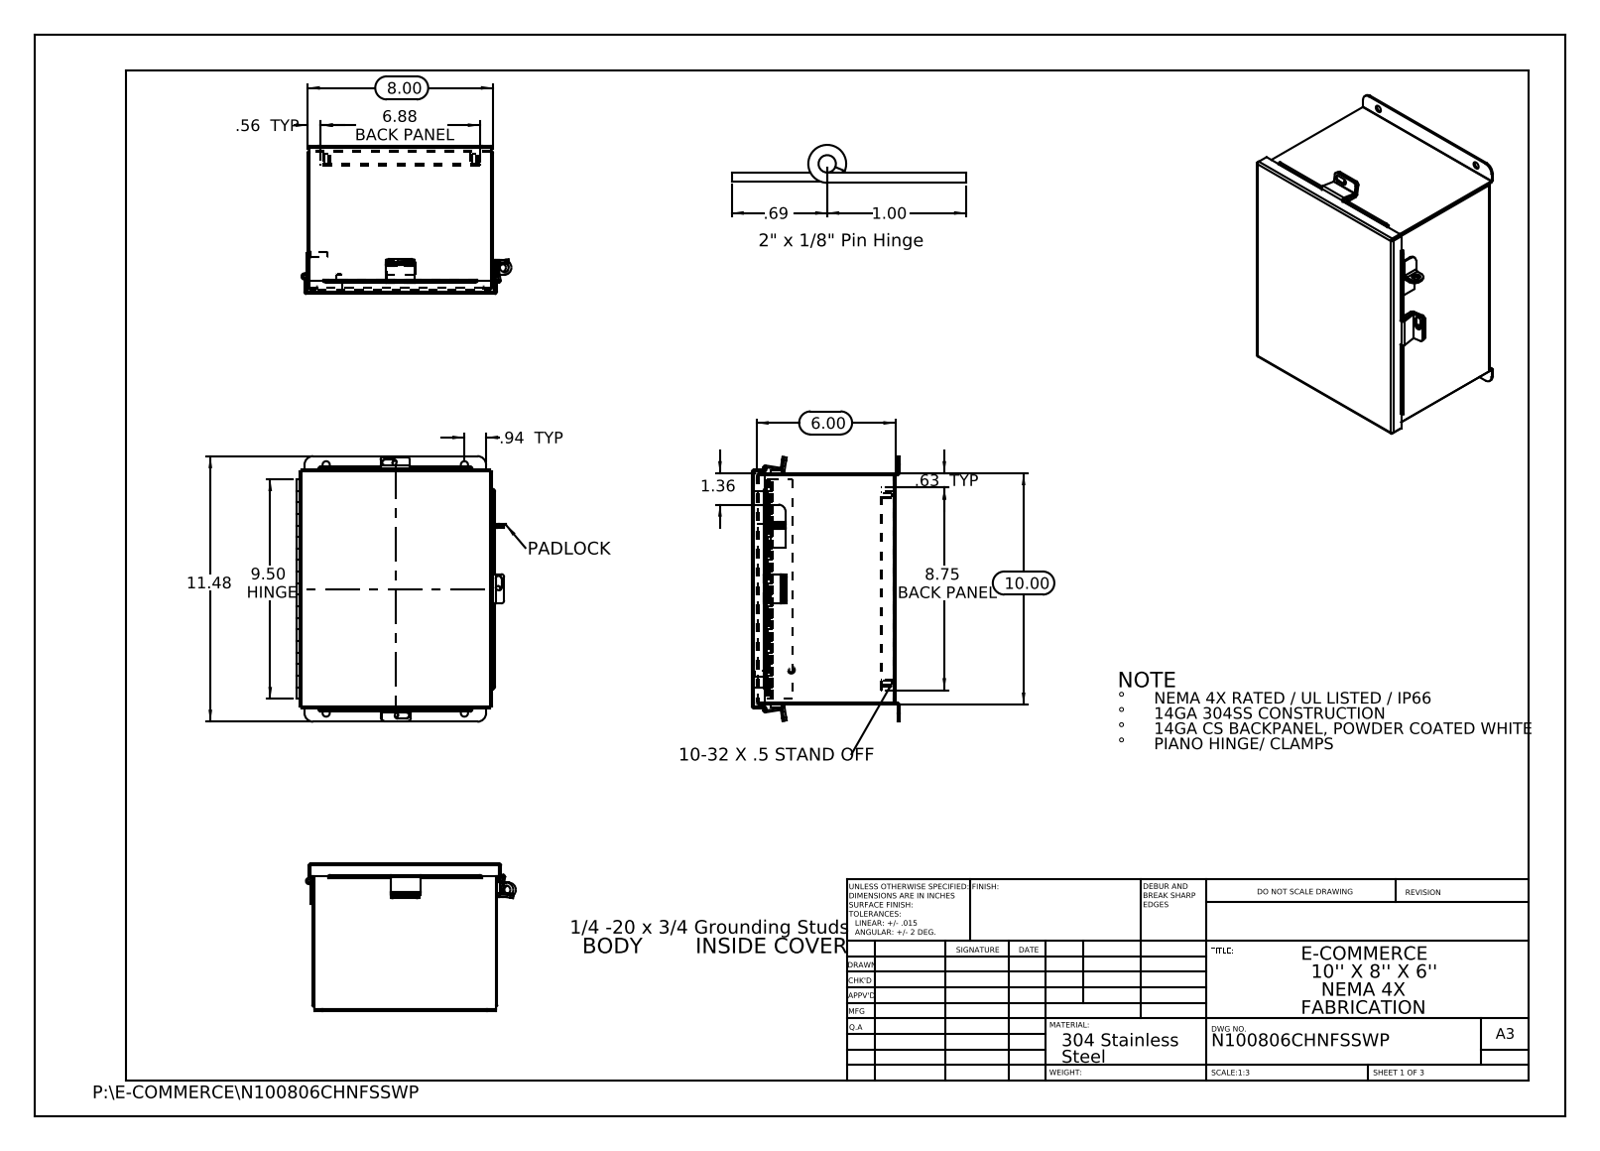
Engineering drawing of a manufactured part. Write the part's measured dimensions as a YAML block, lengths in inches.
part_name: "N100806CHNFSSWP Hinge Body Side; HW-CLH-JH-20104; N100806CHNFSSWP _JIC Hinge; N100806CHNFSSWP JIC Backpanel (+8 more)"
step_written_by: "SolidWorks 2013 (CONFIG_CONTROL_DESIGN)"
units: inches
bodies: {solids: 21, faces: 620, planar: 383, cylindrical: 217, other: 20}
overall_size: [11.476, 9.072, 6.39]
volume: 38.22
surface_area: 1047
round_holes:
  - {diameter: 0.25, count: 7}
  - {diameter: 0.187, count: 4}
  - {diameter: 0.312, count: 4}
  - {diameter: 0.125, count: 1}
  - {diameter: 0.373, count: 1}
  - {diameter: 0.375, count: 1}
round_bosses_or_shafts:
  - {diameter: 0.313, count: 4}
  - {diameter: 0.315, count: 2}
  - {diameter: 0.236, count: 2}
  - {diameter: 0.273, count: 1}
  - {diameter: 0.25, count: 1}
partial_cylinders:
  - {radius: 0.013, count: 13}
  - {radius: 0.009, count: 12}
  - {radius: 0.088, count: 12}
  - {radius: 0.125, count: 10}
  - {radius: 0.083, count: 6}
  - {radius: 0.1, count: 6}
  - {radius: 0.133, count: 6}
  - {radius: 0.375, count: 4}
face_to_face_distances: [0.075, 6.128, 7.925, 9.925, 6.053, 6.203, 0.074, 0.575, 0.5, 5.553]
hole_center_spacings: [1.315, 6.311, 9.428, 11.269, 5.976, 6.375, 8.126, 10.328]
